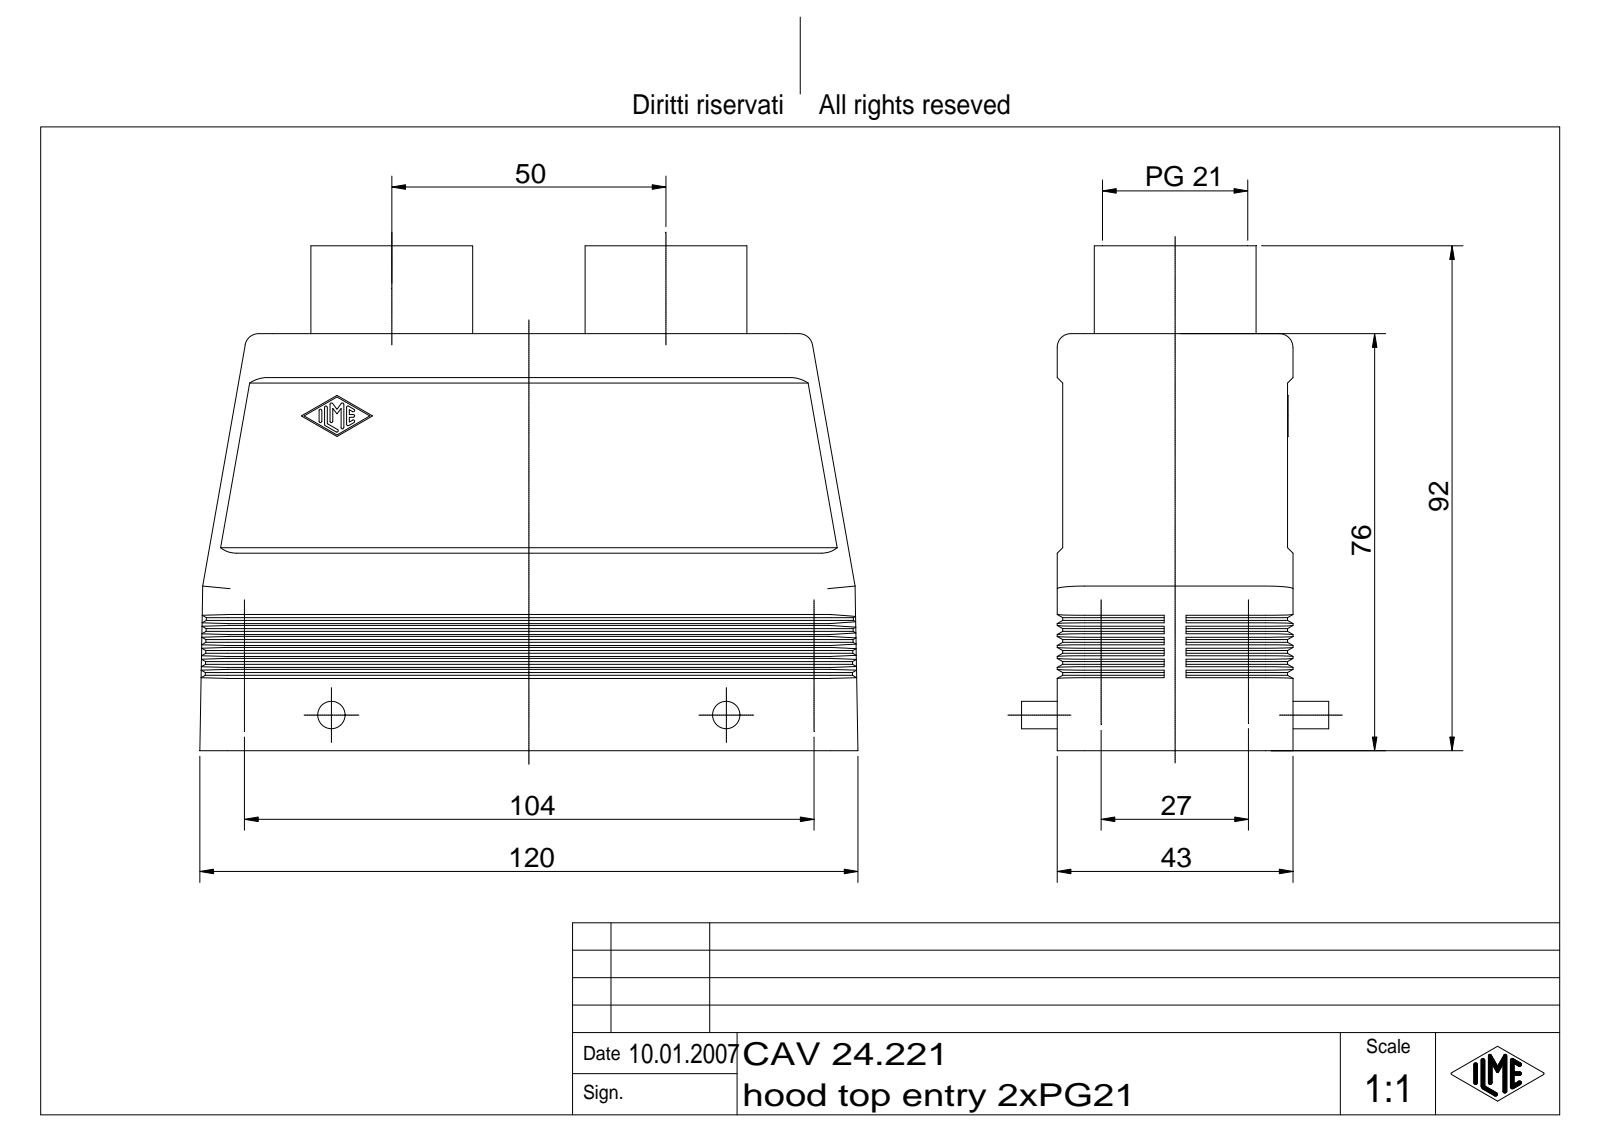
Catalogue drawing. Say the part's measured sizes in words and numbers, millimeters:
The part is named "CAV 24.221". Its 3-D file was written by "Autodesk Inventor 7 (AUTOMOTIVE_DESIGN)". It is 1 solid with 456 faces: 150 planar, 136 cylindrical and 170 other. Overall it measures 120 by 92 by 56 millimeters. Its volume is 81 936 cubic millimeters and its surface area 60 576 square millimeters. Round holes: 2 of diameter 24.5, 1 of diameter 26.5, 1 of diameter 28. Round bosses or shafts: 2 of diameter 5, 1 of diameter 29.5. Partial cylindrical surfaces (rounded edges, fillets, slot ends): 14 of radius 0.25, 12 of radius 4, 8 of radius 2, 8 of radius 5, 4 of radius 2.5, 4 of radius 3.5. The main face-to-face distances are 3, 37, 2, 39, 1, 40, 42, 43, 41, 1.73. The hole center spacings are 50.
